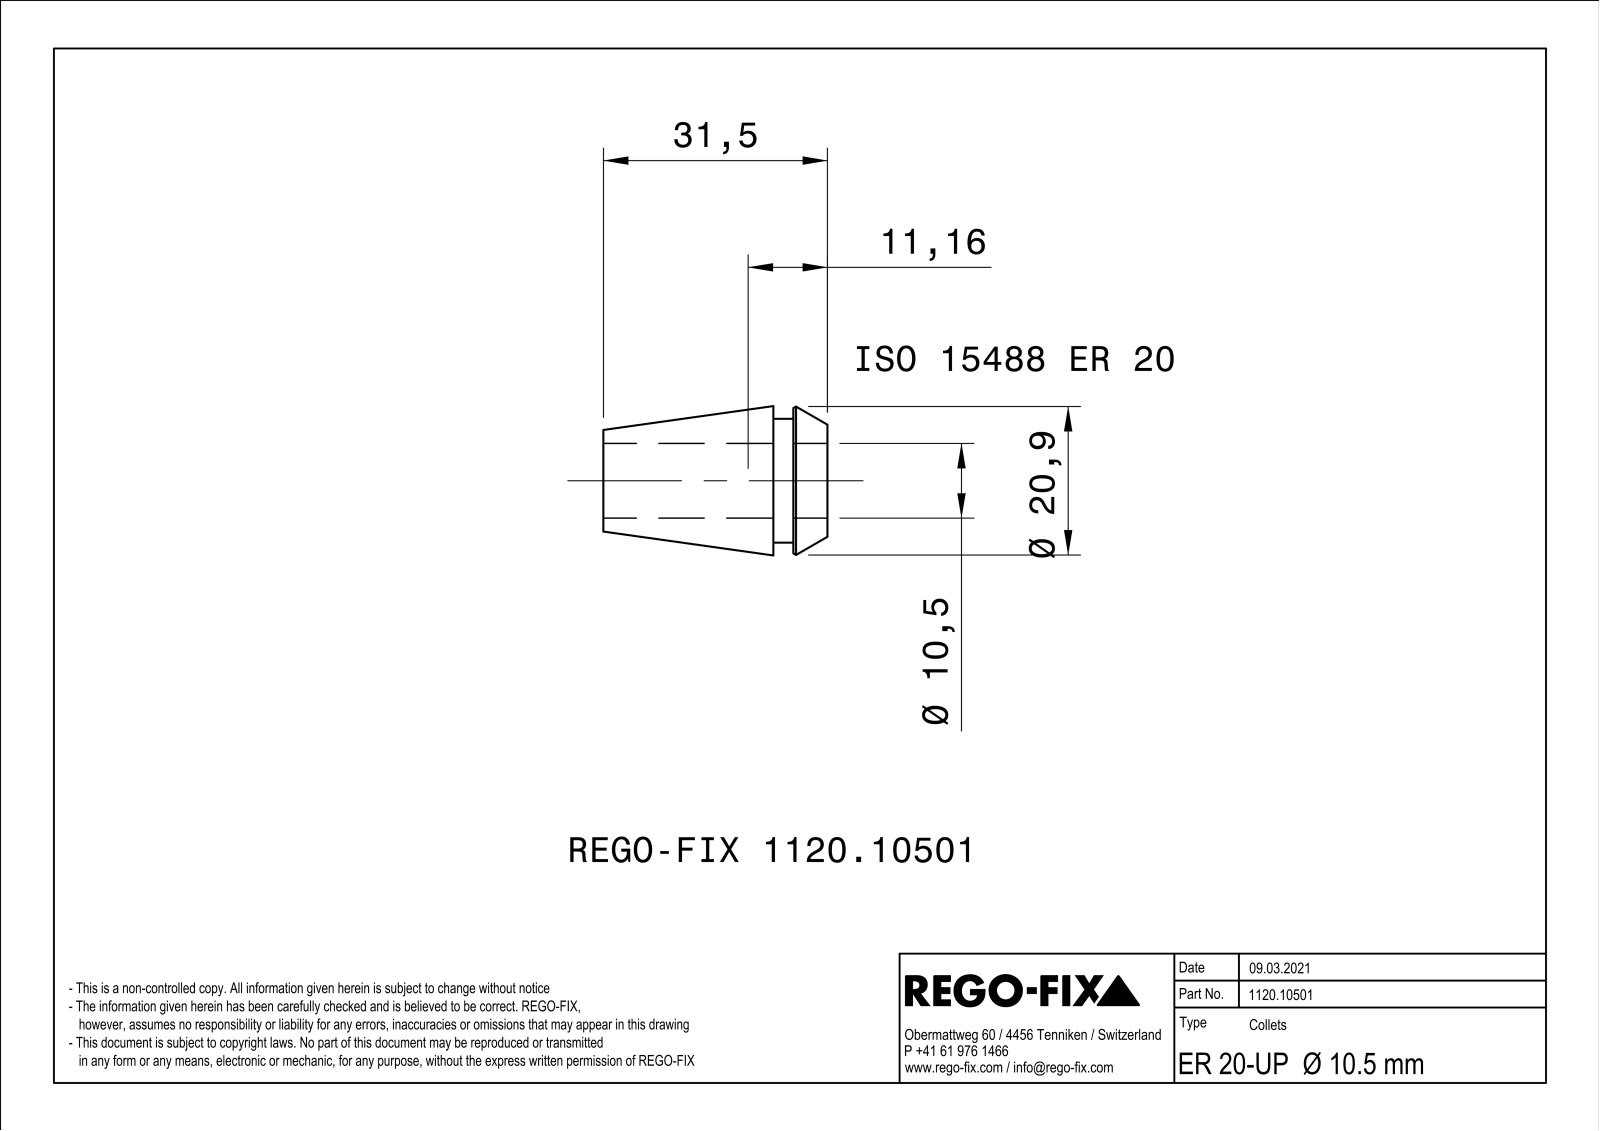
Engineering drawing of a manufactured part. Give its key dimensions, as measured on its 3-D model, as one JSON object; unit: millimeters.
{"part_name": "NOCUT", "step_written_by": "SIEMENS PLM Software Solid Edge ST10 (AUTOMOTIVE_DESIGN)", "units": "millimeters", "bodies": {"solids": 1, "faces": 177, "planar": 88, "cylindrical": 9, "other": 80}, "overall_size": [31.5, 20.99, 20.99], "volume_mm3": 4181, "surface_area_mm2": 5890, "round_holes": [[10.5, 1]], "round_bosses_or_shafts": [[17.4, 1]], "face_to_face_distances": [0.6, 7.6, 4.8, 2.8, 31.5, 26.7, 23.9, 5.5, 0.7, 2.1]}
